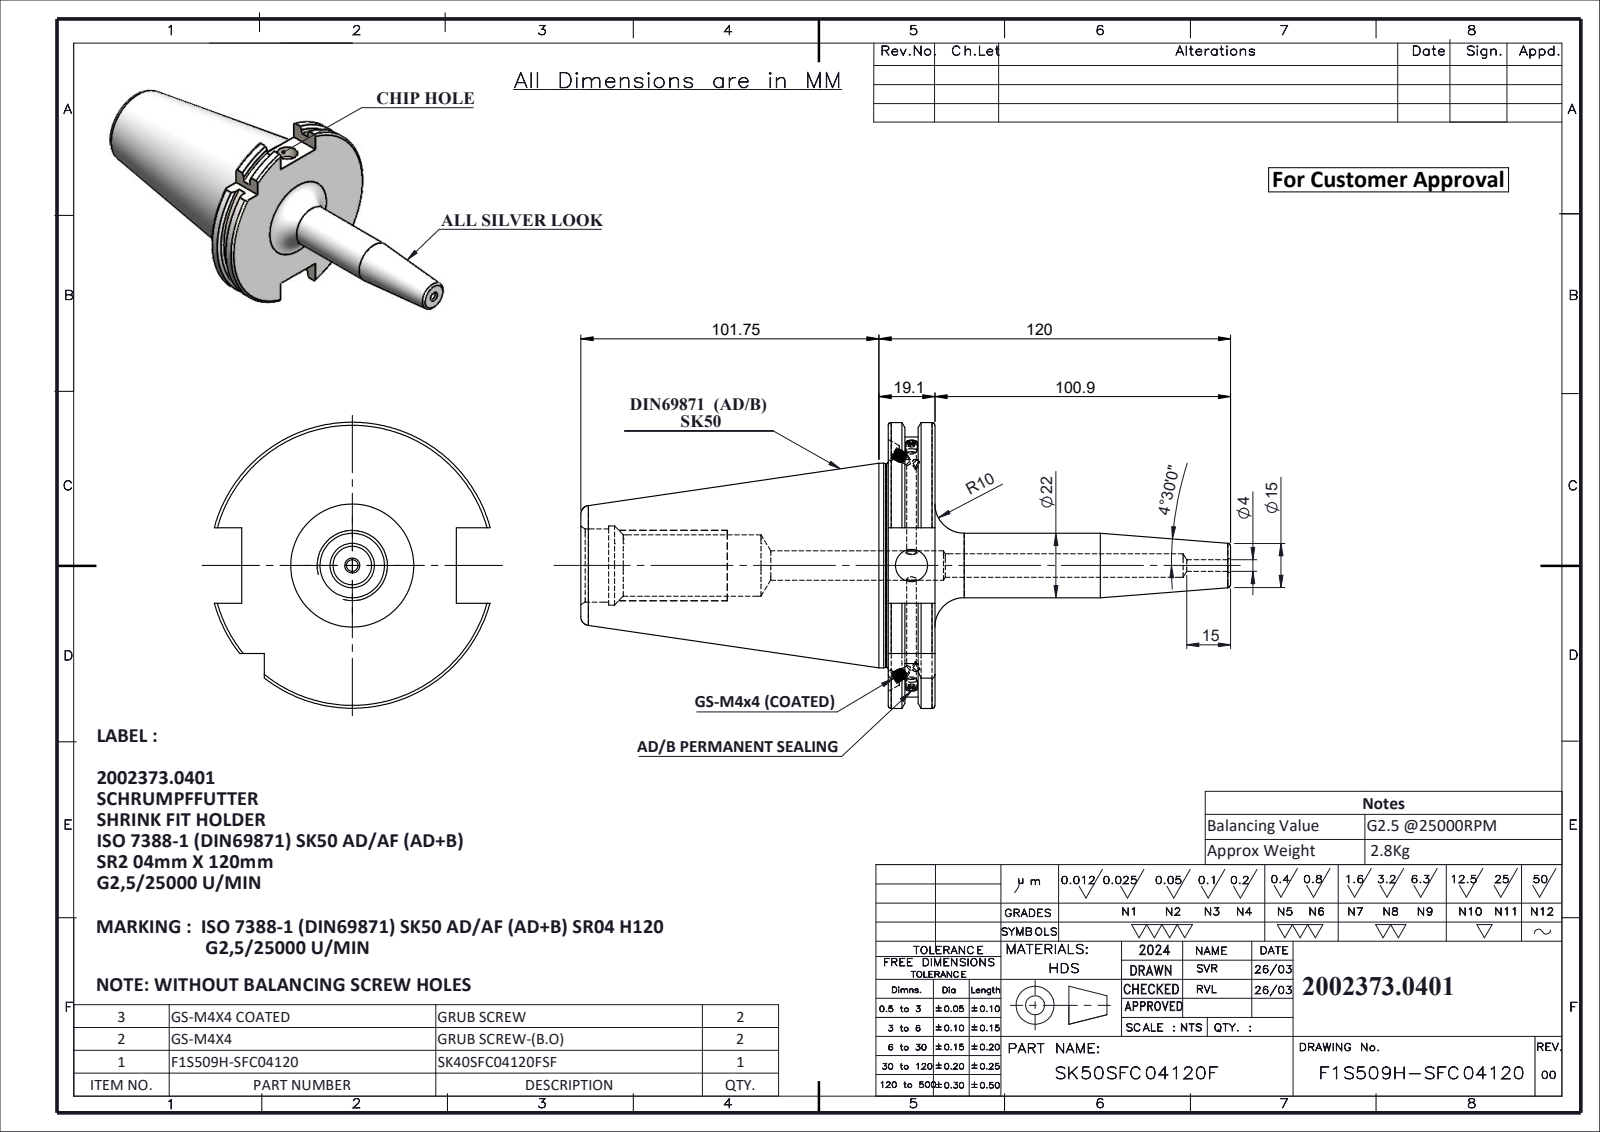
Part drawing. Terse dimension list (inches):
name: GS-M4X4-COATING_DIN 913 - M4 x 4-N; F1S509H-SFC04120; SK50SFC04120FWW; GS-M4X4_DIN 913 - M4 x 4-N
written by: SolidWorks 2024 (CONFIG_CONTROL_DESIGN)
unit: in
bodies: 5 solids, 252 faces (61 planar, 75 cylindrical, 116 other)
size: 8.73 × 3.839 × 3.703
volume: 22.23 in³; area: 80.81 in²
holes: 2× ⌀0.126, 2× ⌀0.236, 1× ⌀0.13, 1× ⌀0.157, 1× ⌀0.315, 1× ⌀0.394, 1× ⌀0.433, 1× ⌀0.827, 1× ⌀0.984, 1× ⌀1.063
bosses: 4× ⌀0.157, 2× ⌀0.114, 1× ⌀2.75, 1× ⌀2.734, 1× ⌀0.866
rounds: 1× R1.768, 1× R1.919
face distances: 0.626, 0.222, 0.404, 0.399, 0.177, 0.227, 4.132, 4.354, 4.531, 4.758
